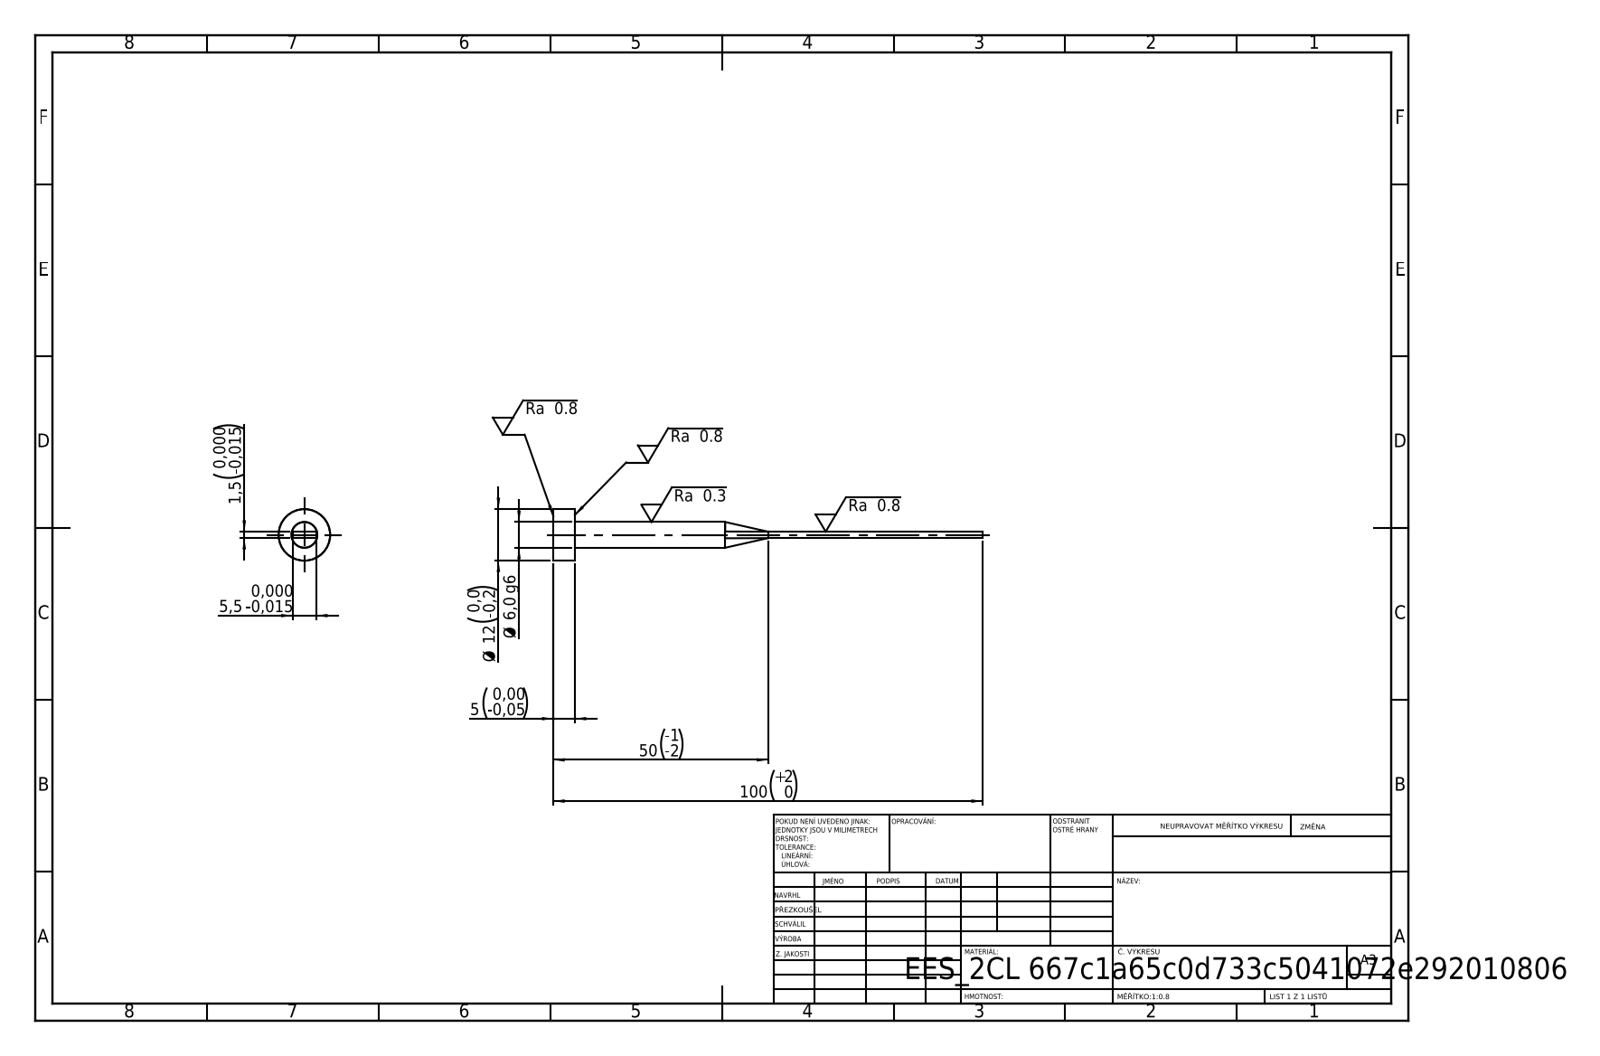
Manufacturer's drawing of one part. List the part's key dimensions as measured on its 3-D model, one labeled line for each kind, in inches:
STEP written by: SolidWorks 2019 (CONFIG_CONTROL_DESIGN)
Units: inches
Bodies: 1 solid, 15 faces (7 planar, 4 cylindrical, 4 other)
Overall size (bounding box): 3.937 × 0.472 × 0.472
Volume: 0.131 in³ · Surface area: 2.967 in²
Round bosses / shafts (diameter × count): ⌀0.472 ×1, ⌀0.236 ×1
Main face-to-face distances: 0.059, 0.197, 0.217, 3.937, 3.74
